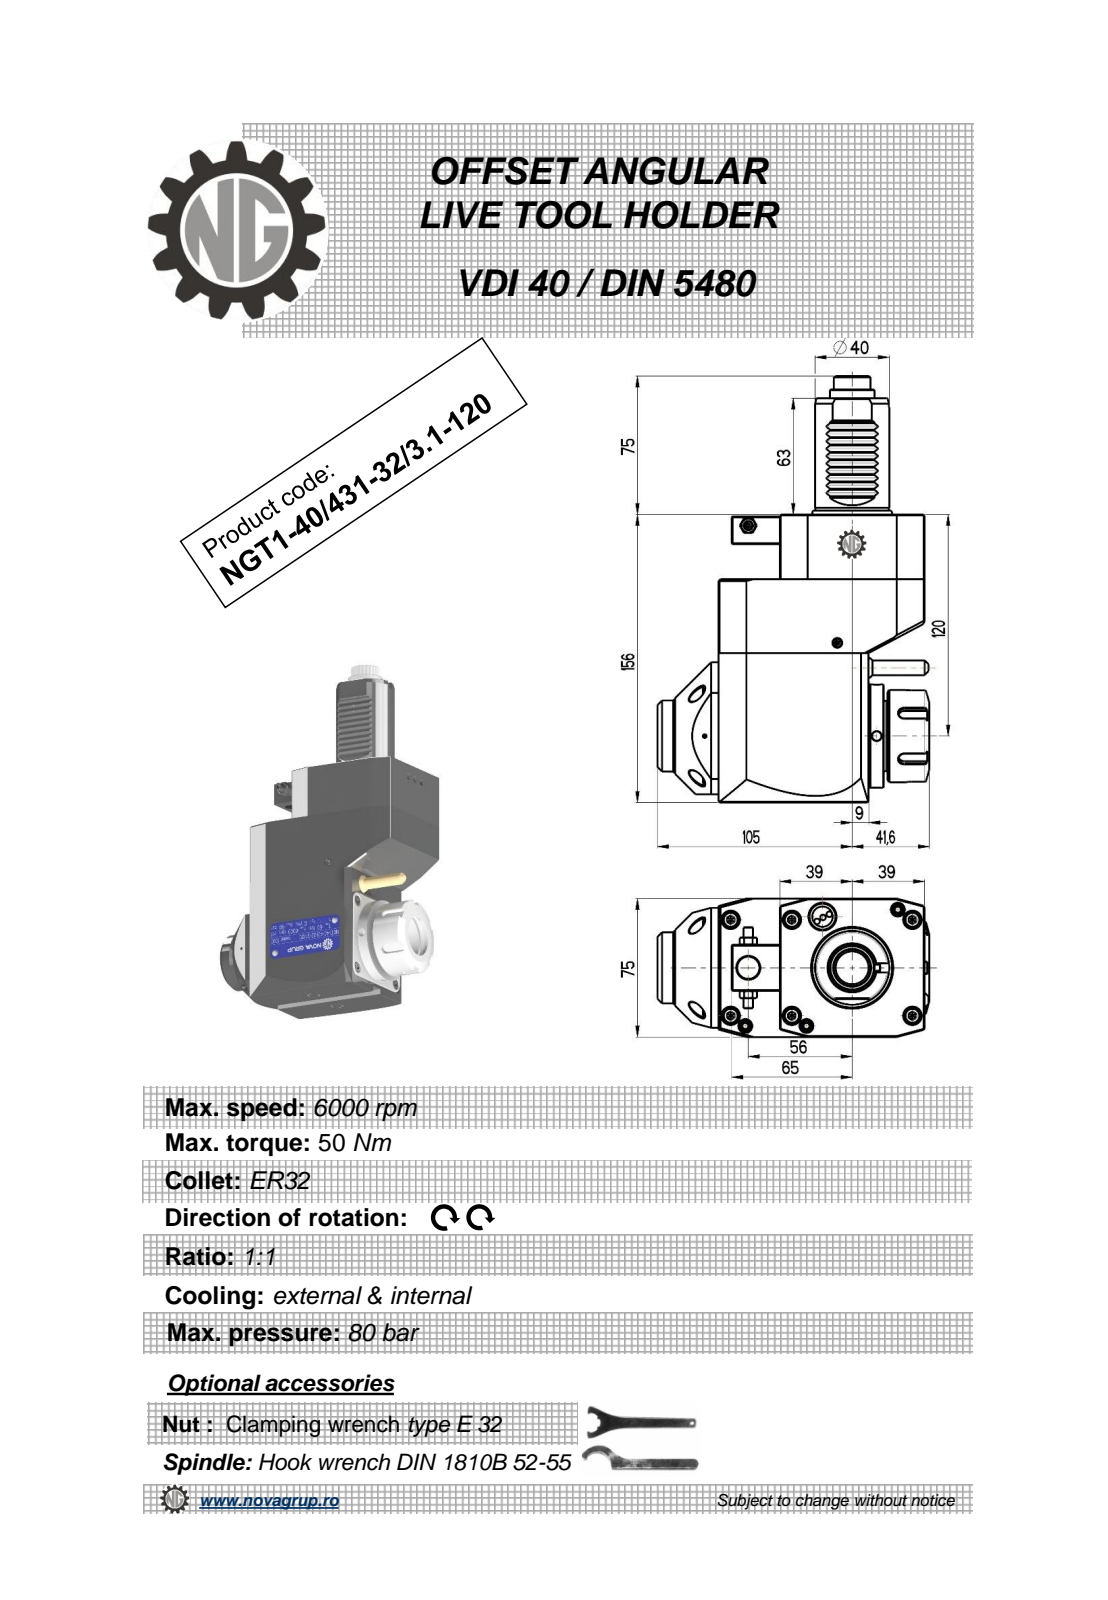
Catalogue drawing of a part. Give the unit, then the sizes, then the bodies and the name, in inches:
Units: inches
Overall size (bounding box): 9.094 × 5.772 × 2.953
Round holes (diameter × count): ⌀0.197 ×3, ⌀0.118 ×1, ⌀0.165 ×1, ⌀0.374 ×1, ⌀0.472 ×1, ⌀1.063 ×1
Round bosses / shafts (diameter × count): ⌀2.205 ×1, ⌀1.969 ×1, ⌀1.693 ×1, ⌀1.575 ×1, ⌀1.516 ×1, ⌀0.945 ×1, ⌀0.441 ×1, ⌀0.353 ×1
Partial cylindrical surfaces — rounded edges, fillets, slot ends (radius × count): R0.082 ×48, R0.01 ×12, R0.012 ×10, R0.009 ×6, R0.118 ×5, R0.357 ×1, R0.391 ×1, R0.591 ×1
Main face-to-face distances: 2.953, 6.142, 4.37, 1.299, 1.378, 4.764, 1.181, 3.189, 1.89, 3.071
Hole centre spacings: 1.611, 2.726, 3.013, 4.39, 5.252
Volume: 74.69 in³ · Surface area: 140.3 in²
Bodies: 1 solid, 551 faces (207 planar, 183 cylindrical, 161 other)
Part name (STEP PRODUCT): NGT1_40_431_32_3_1_120
STEP written by: PRO/ENGINEER BY PARAMETRIC TECHNOLOGY CORPORATION, 2010280 (CONFIG_CONTROL_DESIGN)
